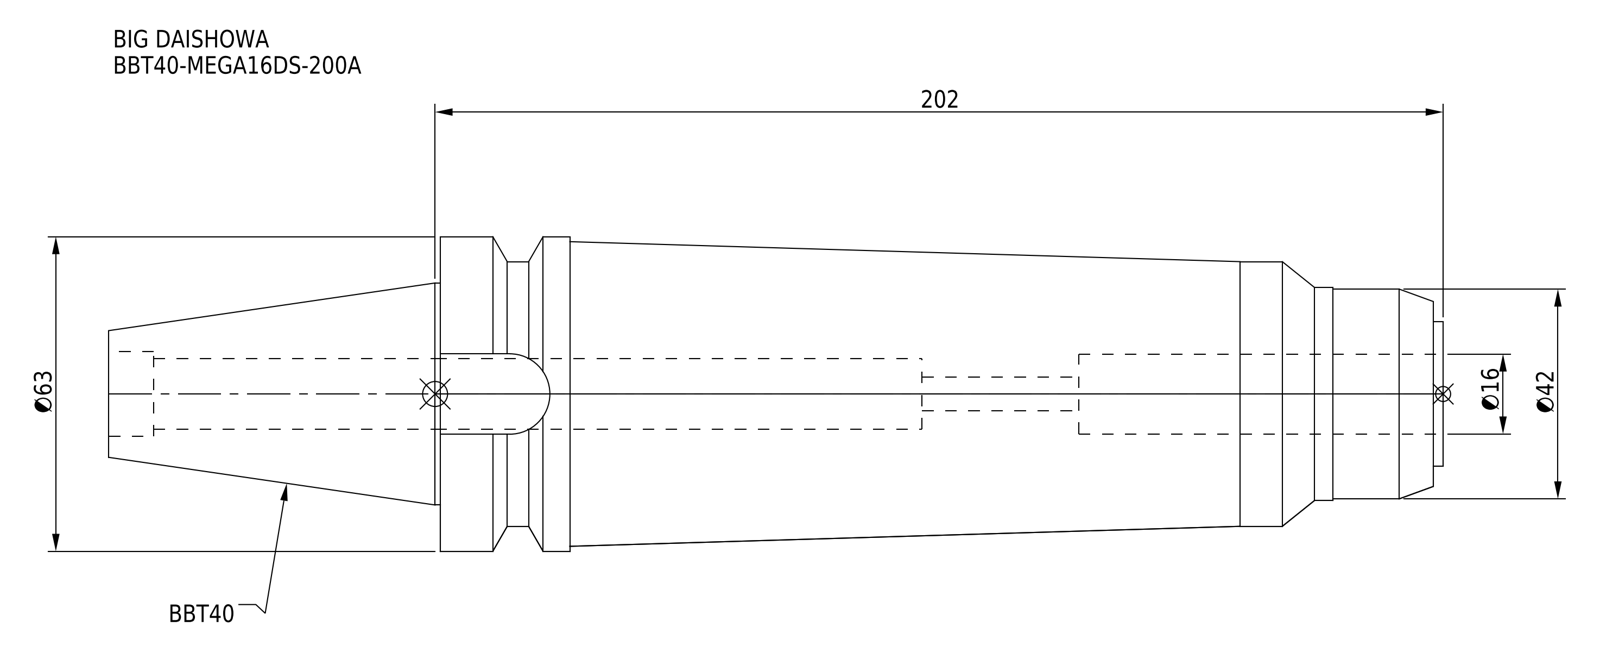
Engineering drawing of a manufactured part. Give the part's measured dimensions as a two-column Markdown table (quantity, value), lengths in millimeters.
| quantity | value |
| --- | --- |
| part name | BBT40-MEGA16DS-200A |
| STEP written by | CREO PARAMETRIC BY PTC INC, 2016380 (AUTOMOTIVE_DESIGN) |
| units | millimeters |
| bodies | 1 solid, 55 faces (15 planar, 28 cylindrical, 12 other) |
| overall size | 267.4 × 63 × 63 |
| volume | 500 289 mm³ |
| surface area | 58 673 mm² |
| round holes (diameter × count) | 6.8 × 1, 14.2 × 1, 16 × 1, 17 × 1 |
| round bosses / shafts (diameter × count) | 63 × 1, 53 × 1, 44.45 × 1, 42.7 × 1, 42 × 1, 29 × 1 |
| partial cylindrical surfaces (radius × count) | 8.05 × 1 |
| main face-to-face distances | 201, 2, 199, 45, 267.4, 265.4, 66.4, 16.1, 175, 173 |
